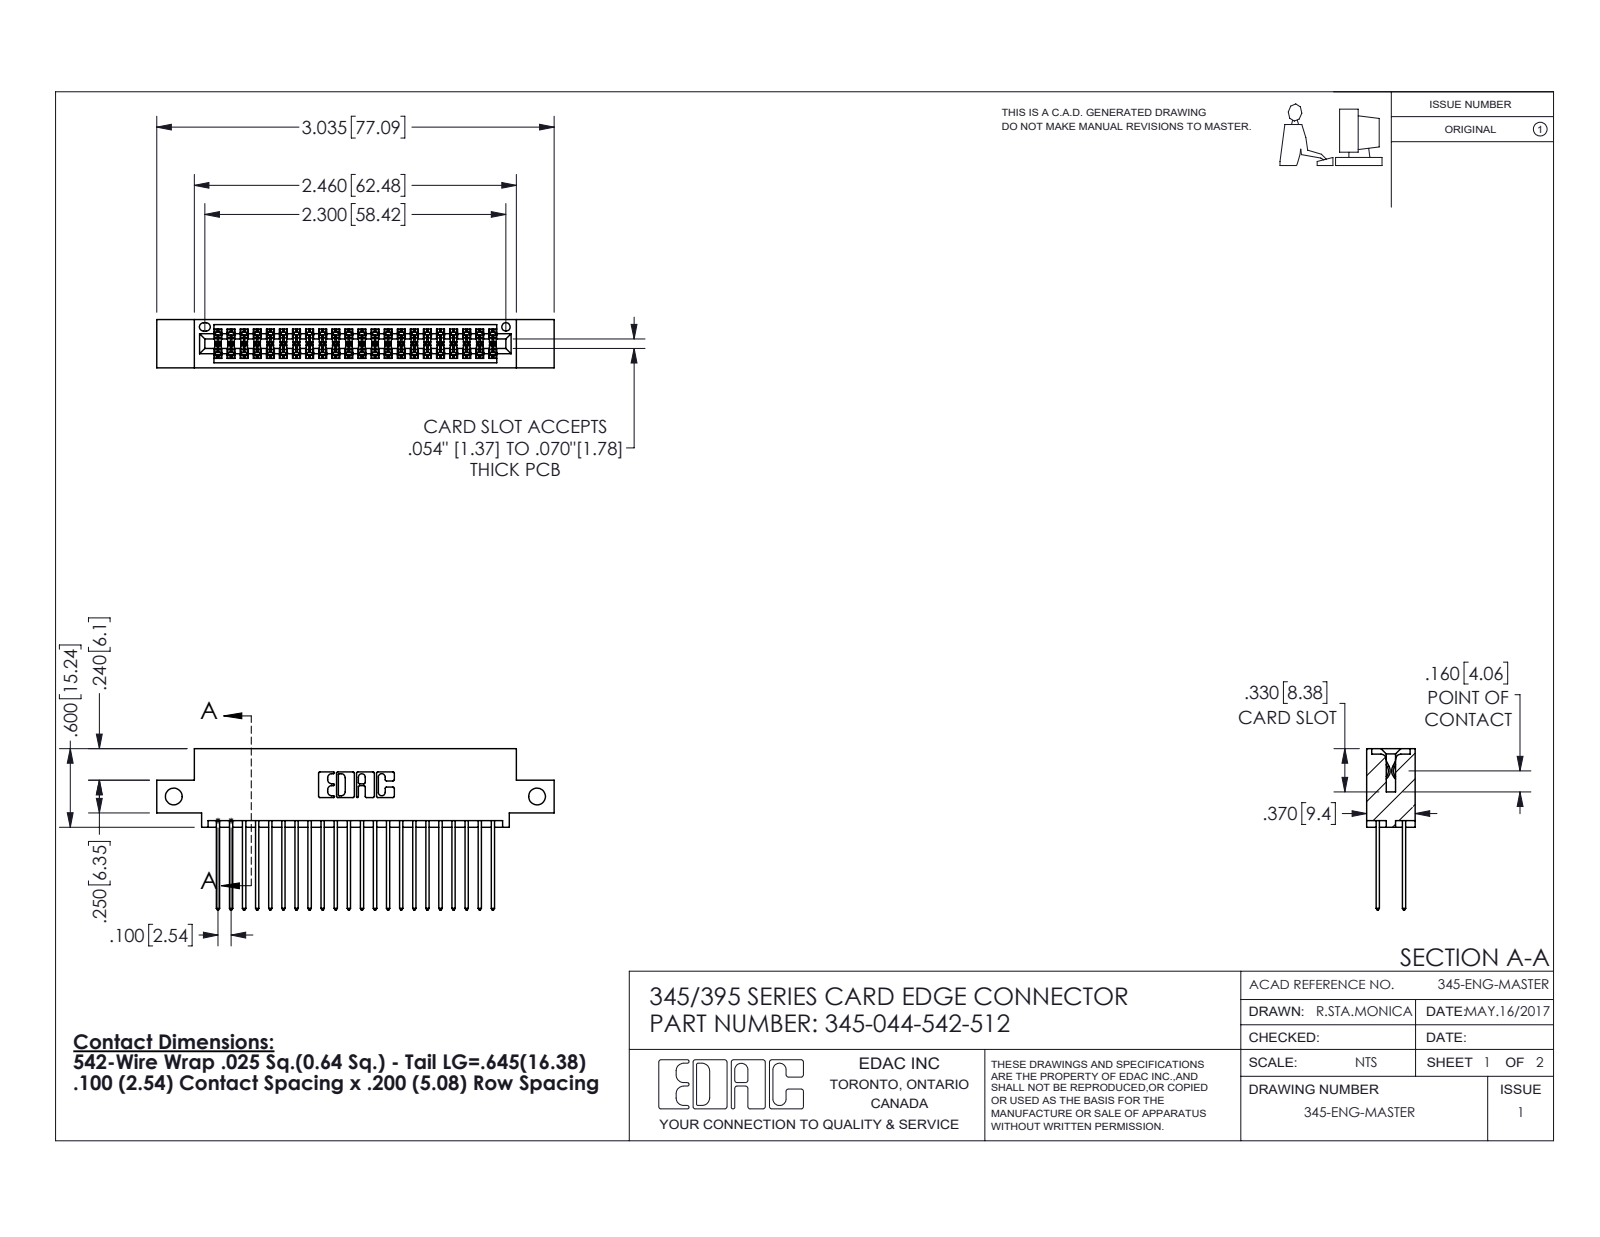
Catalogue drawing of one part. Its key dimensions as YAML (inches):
part_name: "345-044-542-512; 345 Part_0.110 Offset - Side Mount; 345-292-001_345-293-142"
step_written_by: "SolidWorks 2016 (CONFIG_CONTROL_DESIGN)"
units: inches
bodies: {solids: 45, faces: 2330, planar: 1536, cylindrical: 794, other: 0}
overall_size: [3.035, 1.232, 0.37]
volume: 0.448
surface_area: 17.65
round_holes:
  - {diameter: 0.128, count: 2}
  - {diameter: 0.064, count: 1}
partial_cylinders:
  - {radius: 0.006, count: 66}
  - {radius: 0.01, count: 44}
  - {radius: 0.01, count: 22}
  - {radius: 0.007, count: 6}
  - {radius: 0.031, count: 6}
  - {radius: 0.026, count: 3}
  - {radius: 0.014, count: 2}
  - {radius: 0.019, count: 2}
face_to_face_distances: [0.298, 0.072, 0.2, 0.098, 0.272, 0.025, 0.37, 0.225, 0.175, 0.149]
hole_center_spacings: [2.775]
